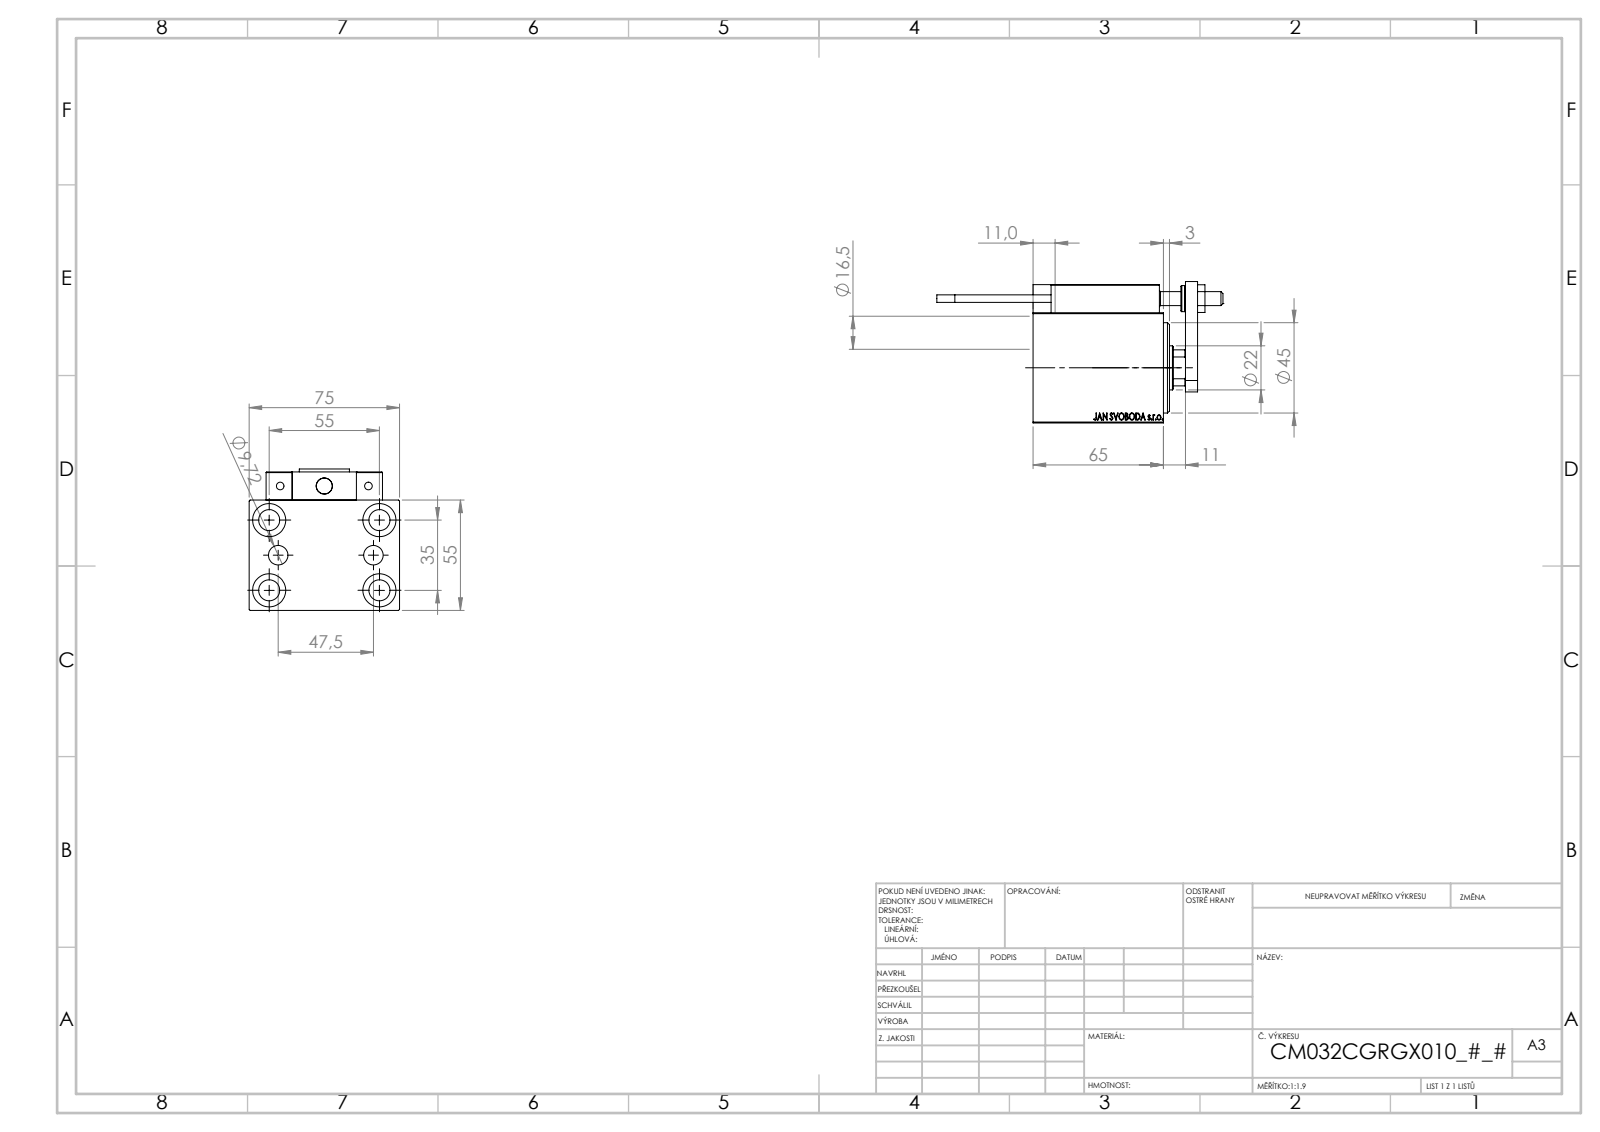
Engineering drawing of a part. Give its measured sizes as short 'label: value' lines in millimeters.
name: MAGNET; KONCOVKA; SWITCH DIM B,W; ZARAZKA (+7 more)
written by: SolidWorks 2019 (CONFIG_CONTROL_DESIGN)
unit: mm
bodies: 23 solids, 1278 faces (560 planar, 184 cylindrical, 534 other)
size: 142.7 × 75 × 70.5
volume: 280 211 mm³; area: 74 686 mm²
holes: 6× ⌀4, 5× ⌀8, 5× ⌀10.5, 5× ⌀16.5, 4× ⌀3.2, 2× ⌀5, 2× ⌀9.72, 1× ⌀7, 1× ⌀22, 1× ⌀25.5, 1× ⌀32, 1× ⌀34
bosses: 2× ⌀5, 2× ⌀3.8, 1× ⌀13, 1× ⌀11
rounds: 30× R0.3, 2× R3, 1× R10.5
face distances: 55, 75, 14, 5, 10, 45, 23, 18, 9, 69
hole spacings: 17.9, 32.6, 54.16, 11.37, 17.12, 20, 23.75, 27.8
